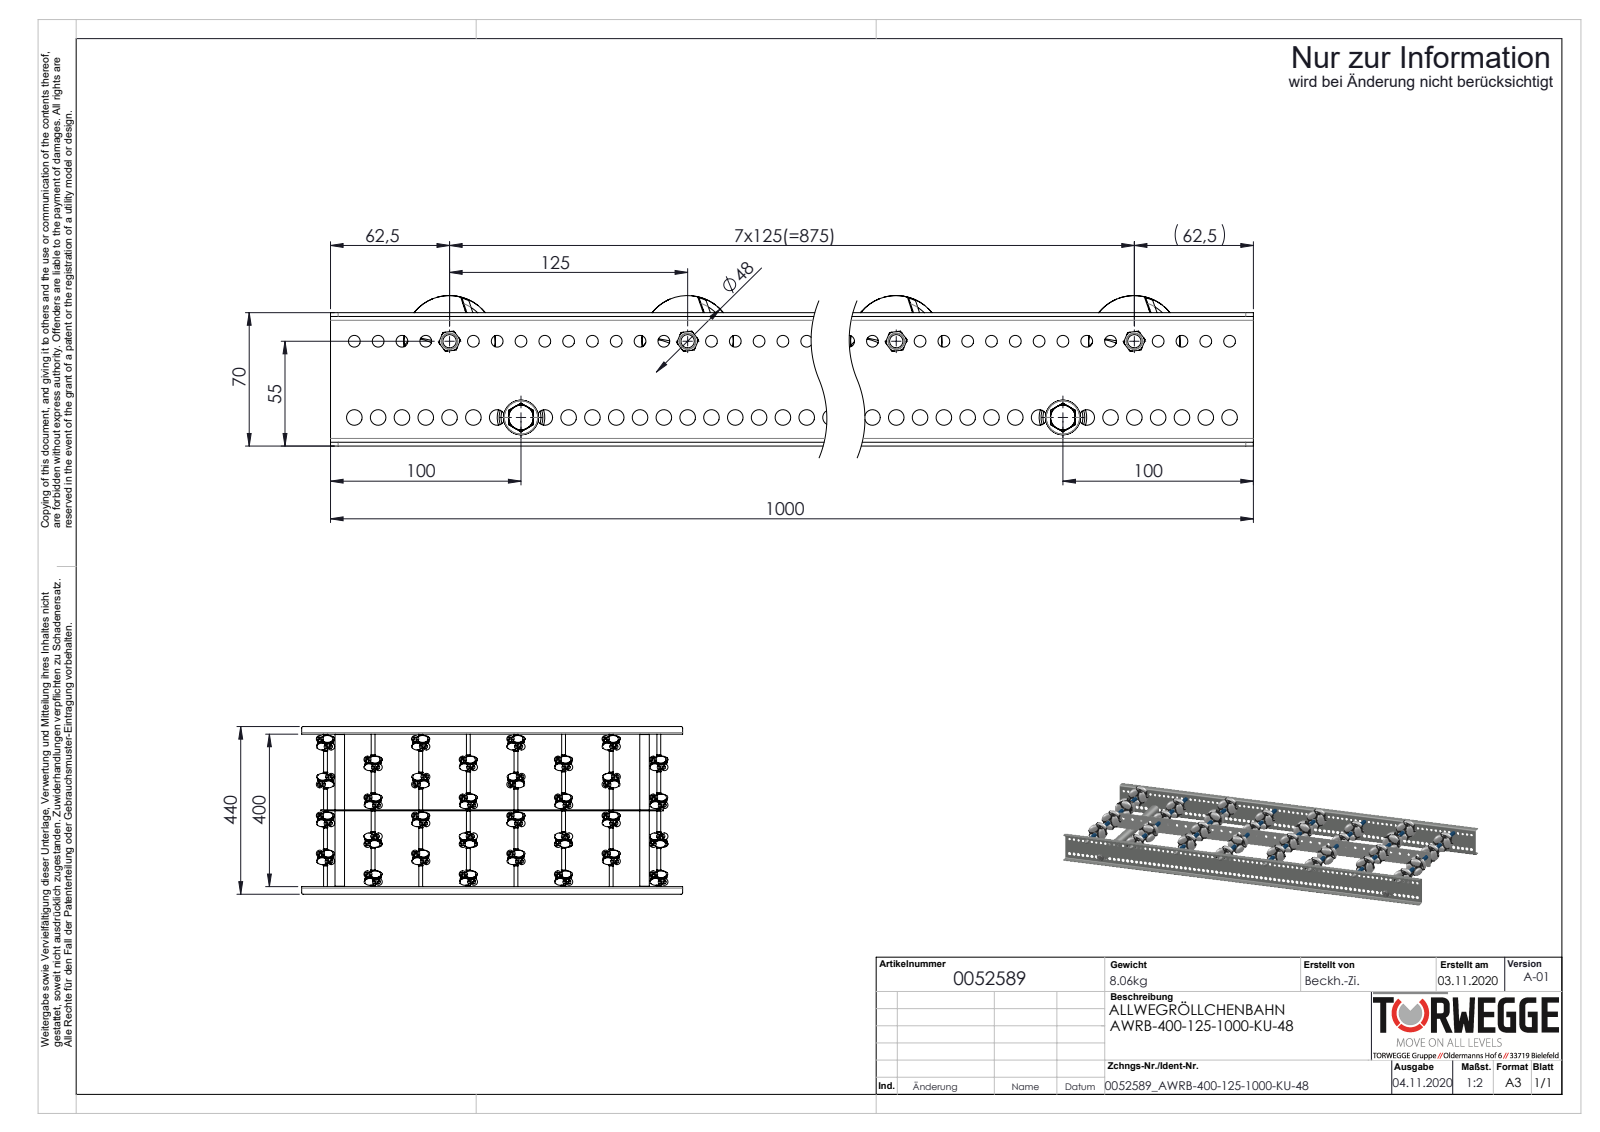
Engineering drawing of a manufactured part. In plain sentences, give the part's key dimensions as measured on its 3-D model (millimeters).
The part is named "AWR48_Stift; S108767_Längstraverse-42x2,5-AWR_L899; AWR-Achse-für-Konfiguration_L400; 0019719_Gewindestange-M6_L=420 (+8 more)". Its 3-D file was written by "SolidWorks 2020 (AUTOMOTIVE_DESIGN)". It is 549 solids with 10226 faces: 3406 planar, 4172 cylindrical and 2648 other. Overall it measures 1000 by 440 by 78.99 millimeters. Its volume is 2 161 000 cubic millimeters and its surface area 1 588 000 square millimeters. Round holes: 192 of diameter 3.7, 192 of diameter 4.2, 79 of diameter 6.2, 79 of diameter 8.2, 36 of diameter 6.5, 8 of diameter 4.92, 8 of diameter 8.4, 2 of diameter 6.8, 2 of diameter 21. Round bosses or shafts: 192 of diameter 4, 162 of diameter 3.7, 10 of diameter 8, 8 of diameter 42, 8 of diameter 11, 8 of diameter 10, 8 of diameter 7, 8 of diameter 6. Partial cylindrical surfaces (rounded edges, fillets, slot ends): 8 of radius 4, 8 of radius 23.55, 4 of radius 2, 4 of radius 5. The main face-to-face distances are 2, 402, 68, 400, 404, 200.6, 198.6, 201.4, 203.4, 203.1. The hole center spacings are 36.06, 36.05, 36.07, 125, 250, 12.5, 36.04, 25.
